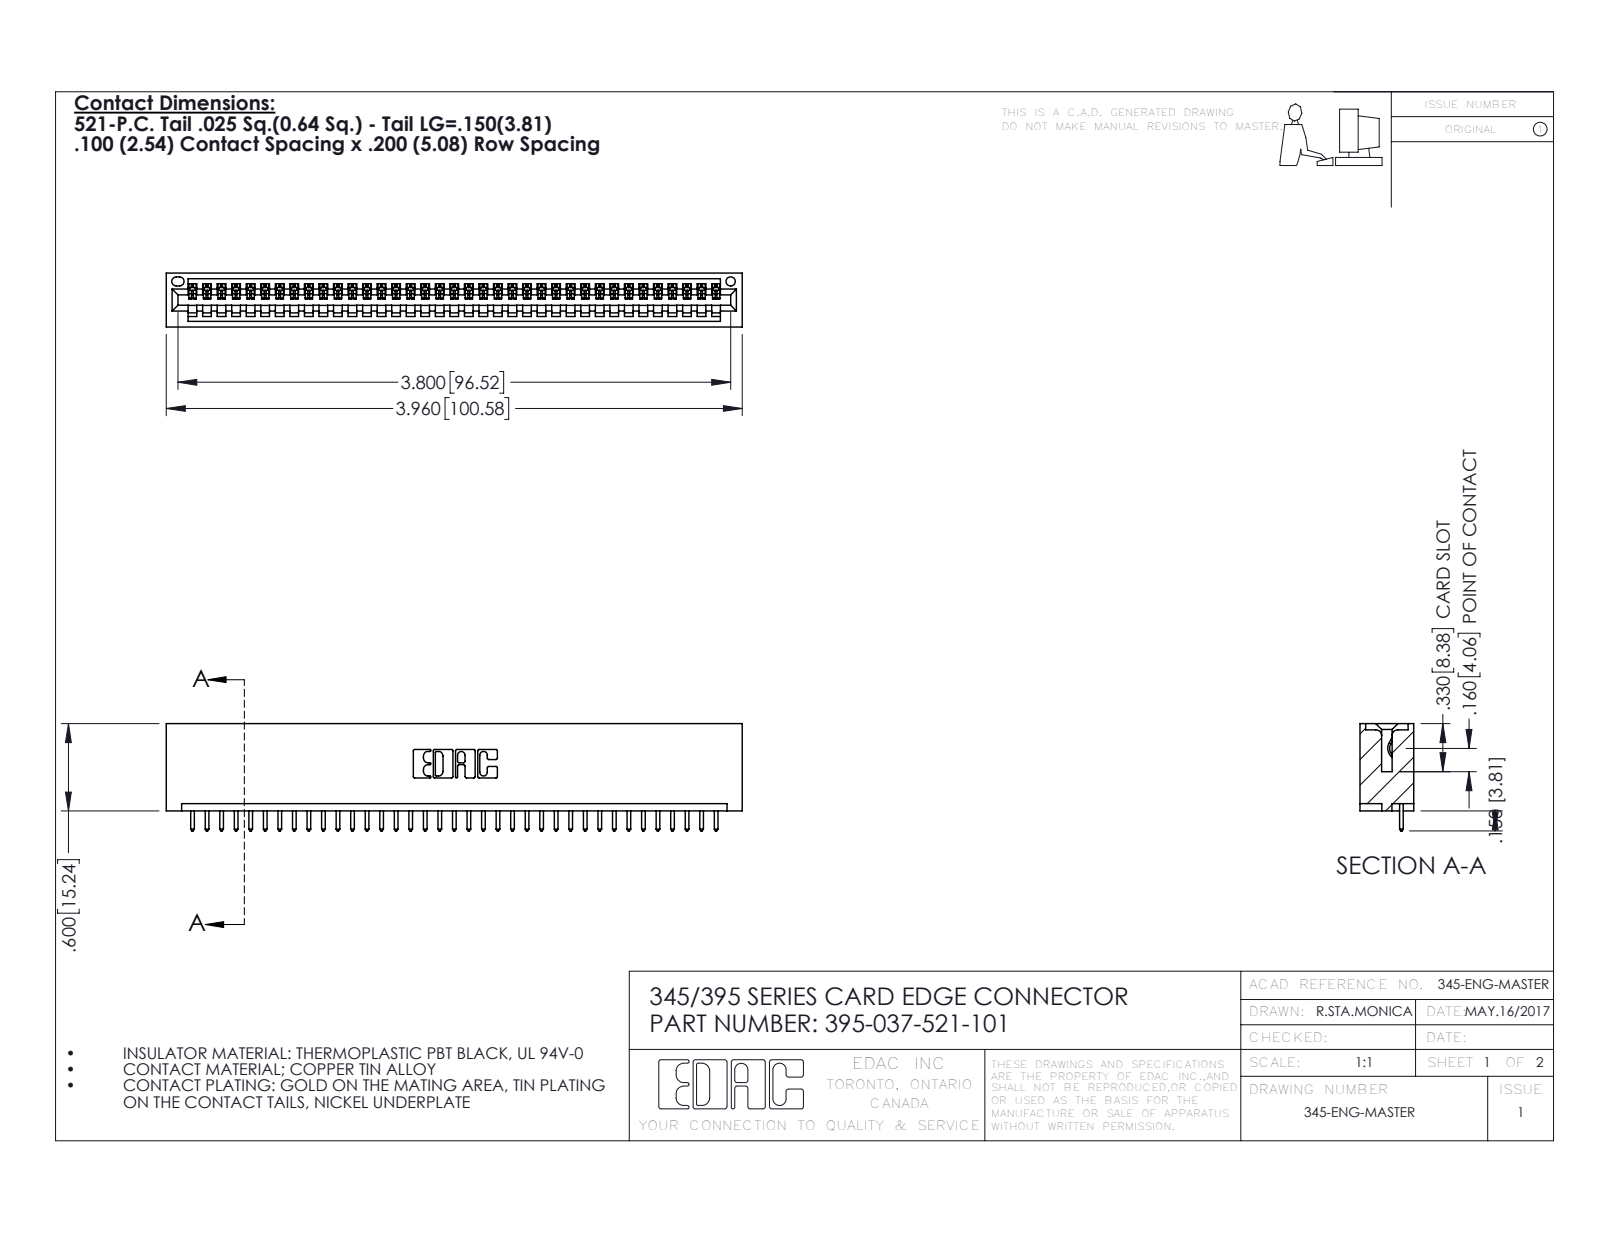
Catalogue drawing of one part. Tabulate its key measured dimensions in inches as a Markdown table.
| quantity | value |
| --- | --- |
| part name | 345-292-001_345-293-121; 395-037-521-101; 345 Part_No Mounting Lugs |
| STEP written by | SolidWorks 2016 (CONFIG_CONTROL_DESIGN) |
| units | inches |
| bodies | 38 solids, 2264 faces (1556 planar, 708 cylindrical, 0 other) |
| overall size | 3.96 × 0.737 × 0.37 |
| volume | 0.61 in³ |
| surface area | 20.13 in² |
| round holes (diameter × count) | 0.064 × 1 |
| partial cylindrical surfaces (radius × count) | 0.006 × 74, 0.01 × 74, 0.01 × 22, 0.007 × 6, 0.031 × 6, 0.026 × 3, 0.031 × 2, 0.04 × 2 |
| main face-to-face distances | 0.298, 0.072, 0.37, 0.2, 0.098, 0.272, 0.025, 0.225, 0.149, 0.072 |
